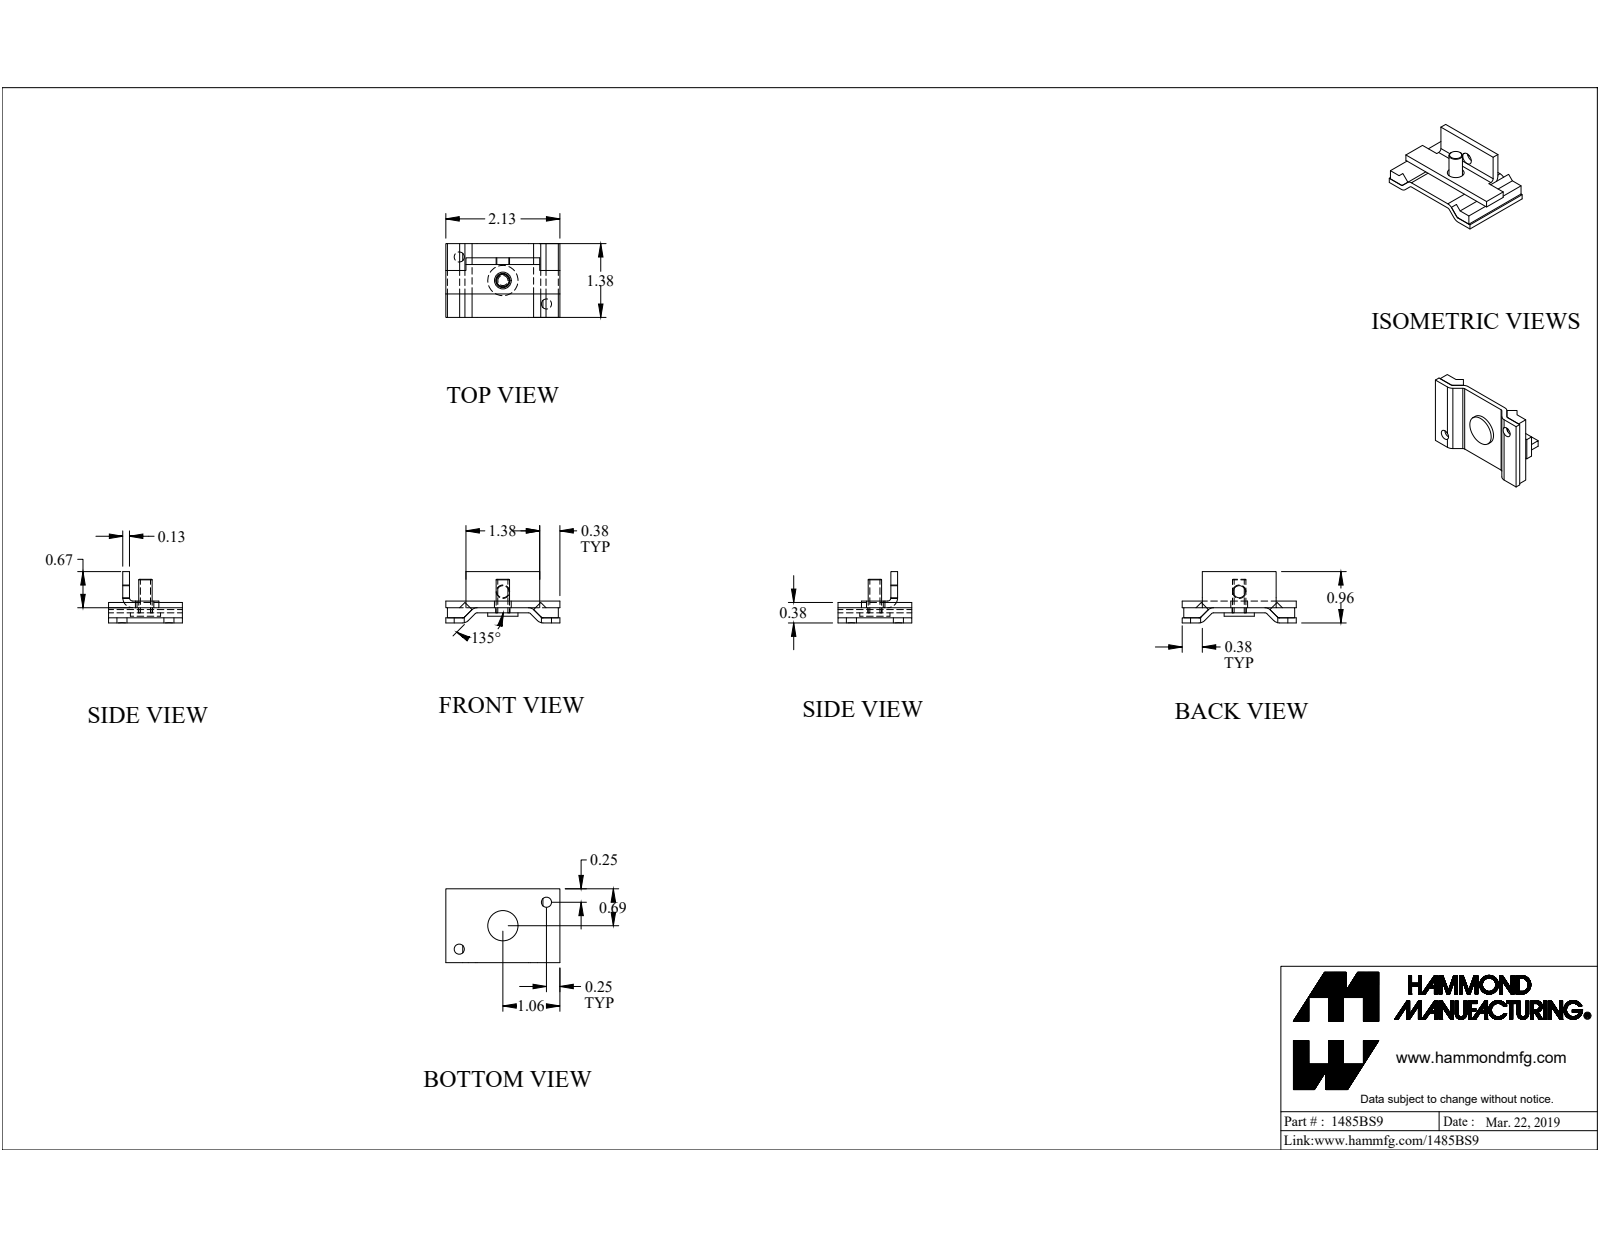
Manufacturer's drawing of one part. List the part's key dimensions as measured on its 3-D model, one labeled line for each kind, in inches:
Part name (STEP PRODUCT): 1485BS9
STEP written by: SolidWorks 2019 (CONFIG_CONTROL_DESIGN)
Units: inches
Bodies: 5 solids, 67 faces (47 planar, 19 cylindrical, 1 other)
Overall size (bounding box): 2.125 × 1.375 × 0.956
Volume: 0.788 in³ · Surface area: 16.47 in²
Round holes (diameter × count): ⌀0.187 ×2, ⌀0.224 ×1, ⌀0.265 ×1, ⌀0.313 ×1
Round bosses / shafts (diameter × count): ⌀0.563 ×1, ⌀0.25 ×1
Partial cylindrical surfaces — rounded edges, fillets, slot ends (radius × count): R0.048 ×4, R0.143 ×4, R0.06 ×1, R0.185 ×1
Main face-to-face distances: 0.188, 0.125, 0.093, 0.095, 0.095, 0.187, 0.313, 0.22, 0.283, 0.407
Hole centre spacings: 0.923, 1.846
